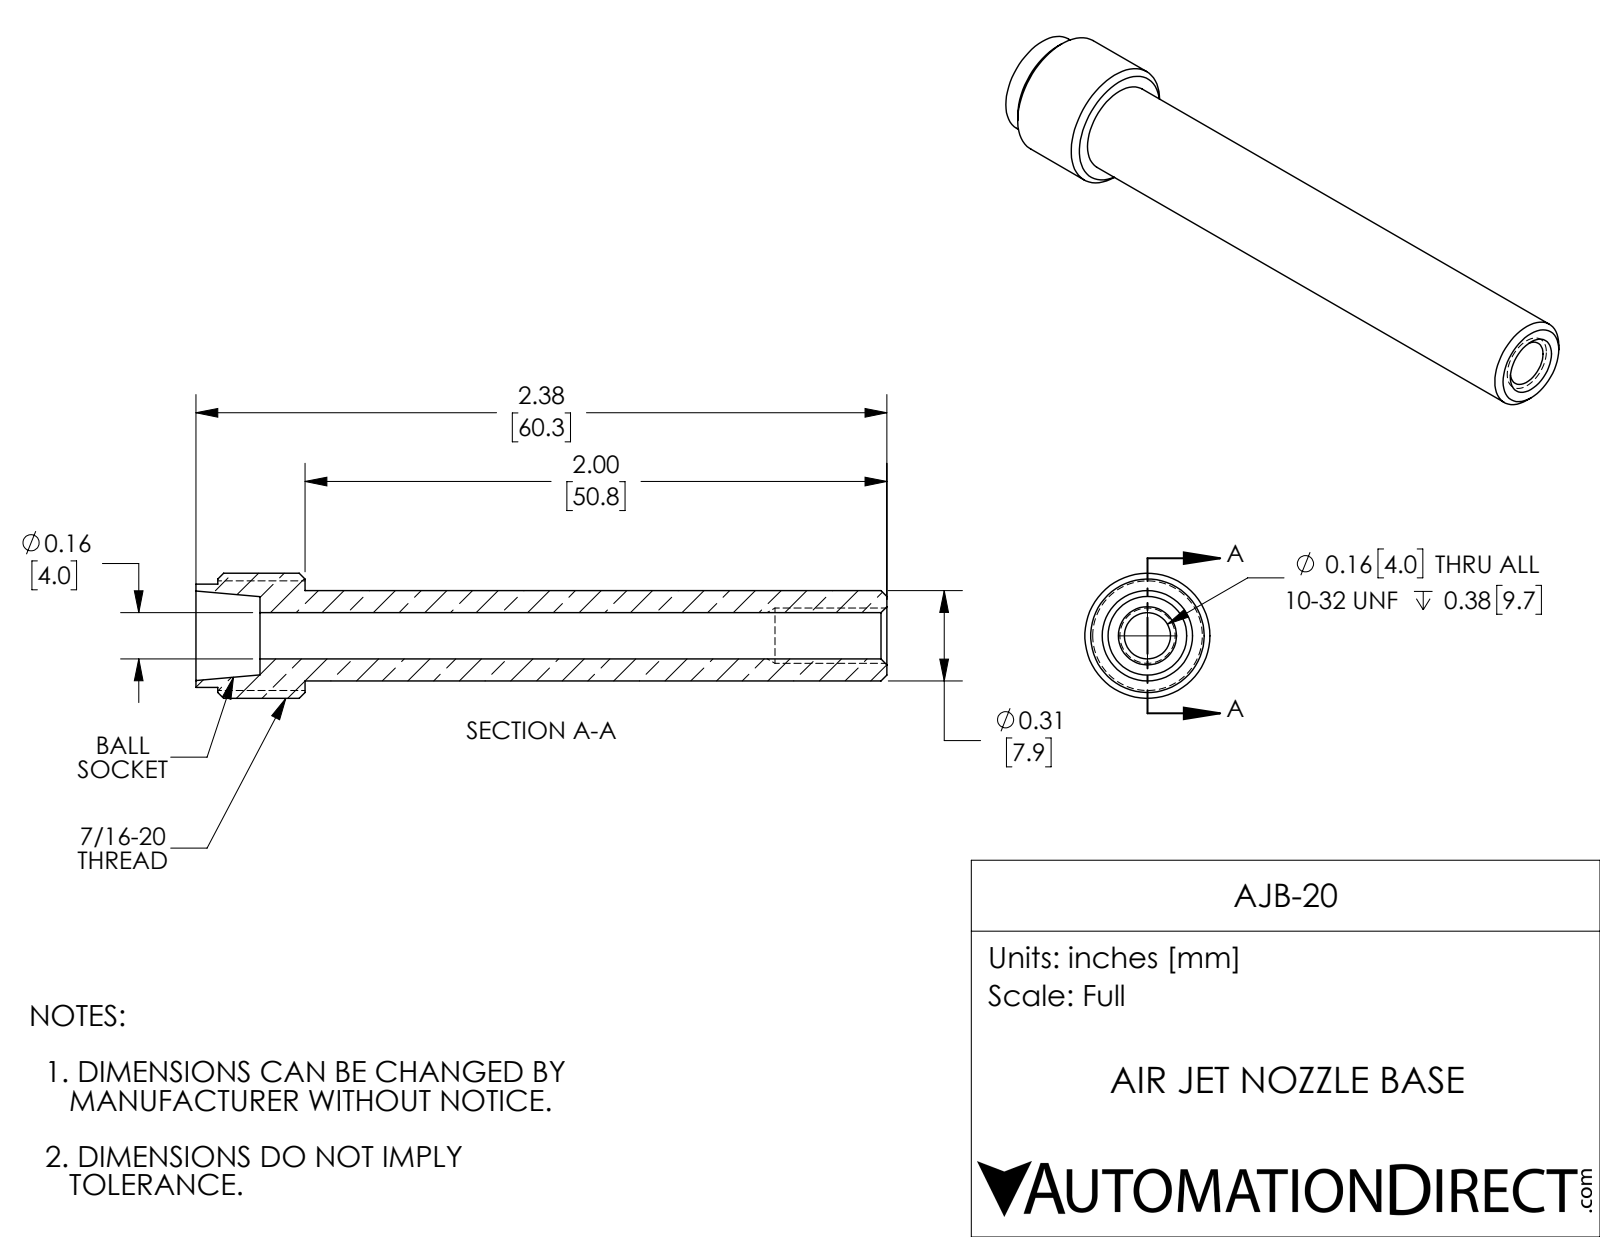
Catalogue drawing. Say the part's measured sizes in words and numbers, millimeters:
The part is named "AJB-20". Its 3-D file was written by "SolidWorks 2018 (AUTOMOTIVE_DESIGN)". It is 1 solid with 23 faces: 5 planar, 8 cylindrical and 10 other. Overall it measures 60.3 by 10.9 by 10.9 millimeters. Its volume is 2 360 cubic millimeters and its surface area 2 515 square millimeters. Round holes: 1 of diameter 4. Round bosses or shafts: 1 of diameter 10.9, 1 of diameter 9, 1 of diameter 7.9. The main face-to-face distances are 3.9, 50.8, 54.7, 60.3, 9.5, 5.6, 58.4, 7.6, 3.7, 1.9.
